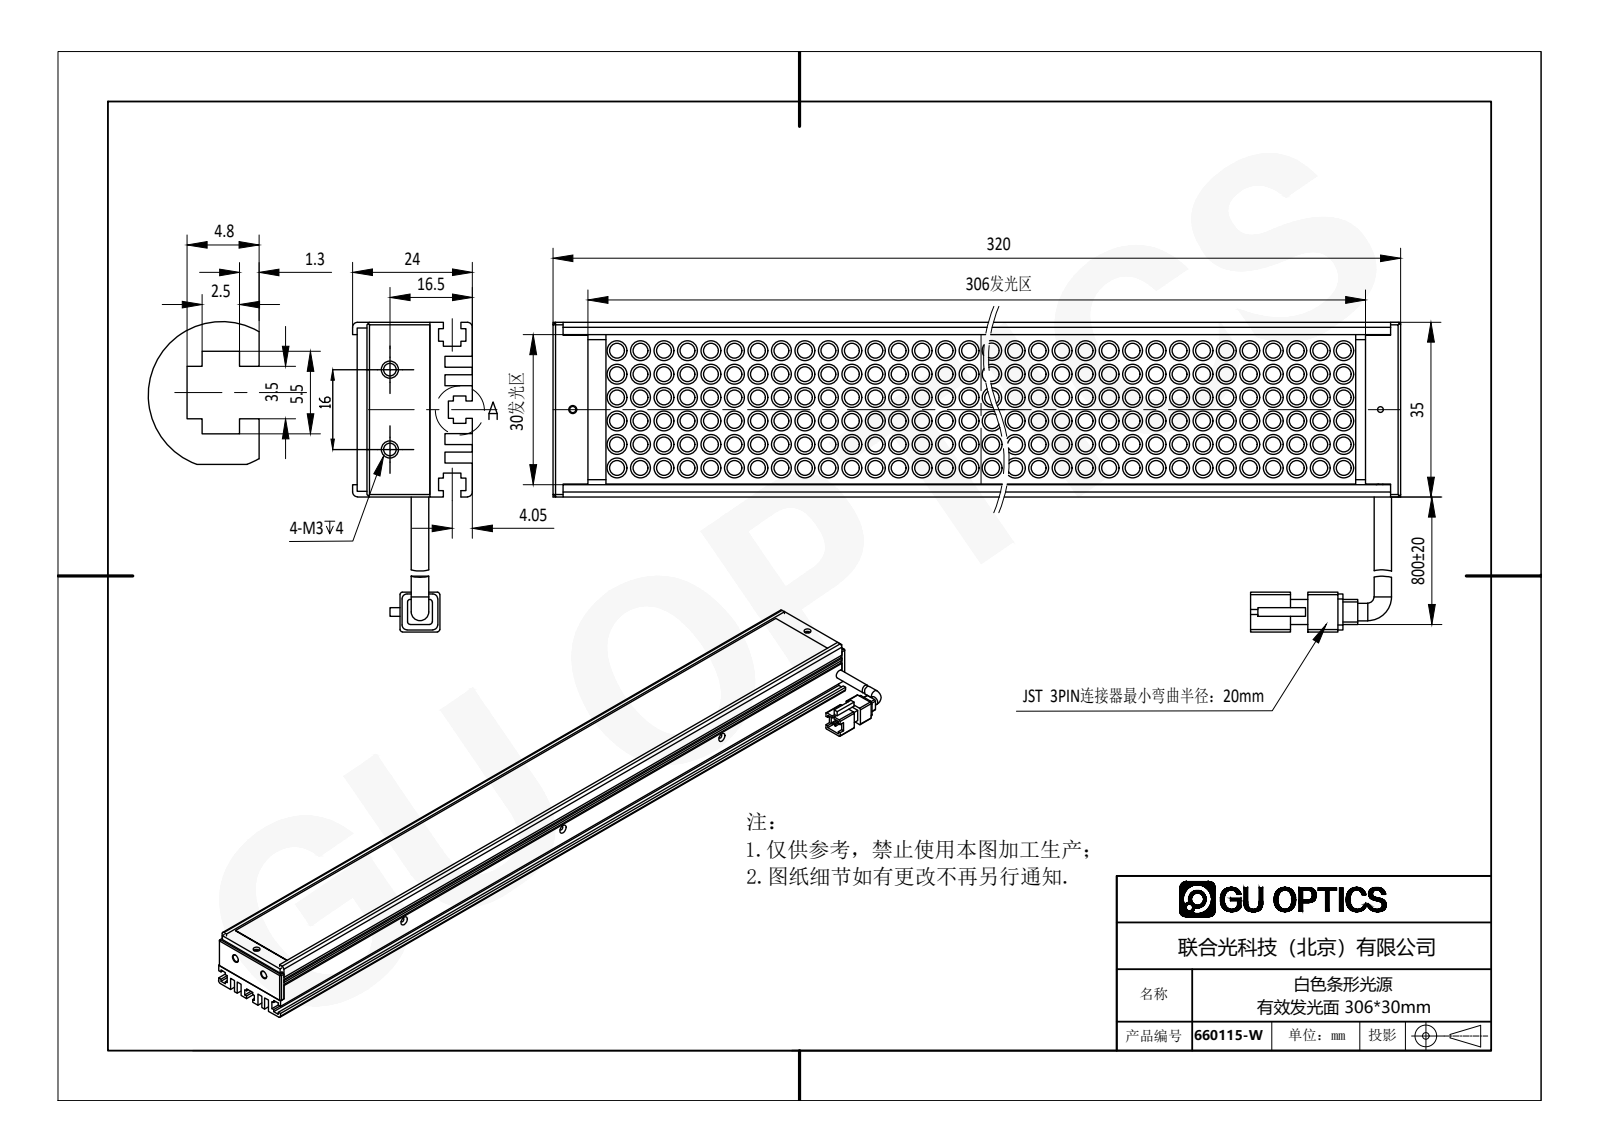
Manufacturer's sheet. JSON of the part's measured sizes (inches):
{"part_name": "660115-W", "step_written_by": "SolidWorks 2016 (AUTOMOTIVE_DESIGN)", "units": "inches", "bodies": {"solids": 11, "faces": 2871, "planar": 733, "cylindrical": 1647, "other": 491}, "overall_size": [12.598, 2.441, 0.945], "volume_in3": 8.586, "surface_area_in2": 251.1, "round_holes": [[0.063, 5], [0.067, 3], [0.059, 2], [0.098, 2], [0.11, 2], [0.118, 2], [0.043, 1], [0.049, 1], [0.079, 1]], "round_bosses_or_shafts": [[0.157, 384], [0.118, 384], [0.138, 2]], "partial_cylinders_radius": [[0.039, 28], [0.02, 8], [0.065, 1]], "face_to_face_distances": [0.079, 0.087, 0.441, 0.039, 0.098, 0.496, 0.575, 0.362, 0.583, 0.335], "hole_center_spacings": [12.283, 0.276, 2.599, 2.607, 3.543, 6.142, 6.145, 9.685]}
